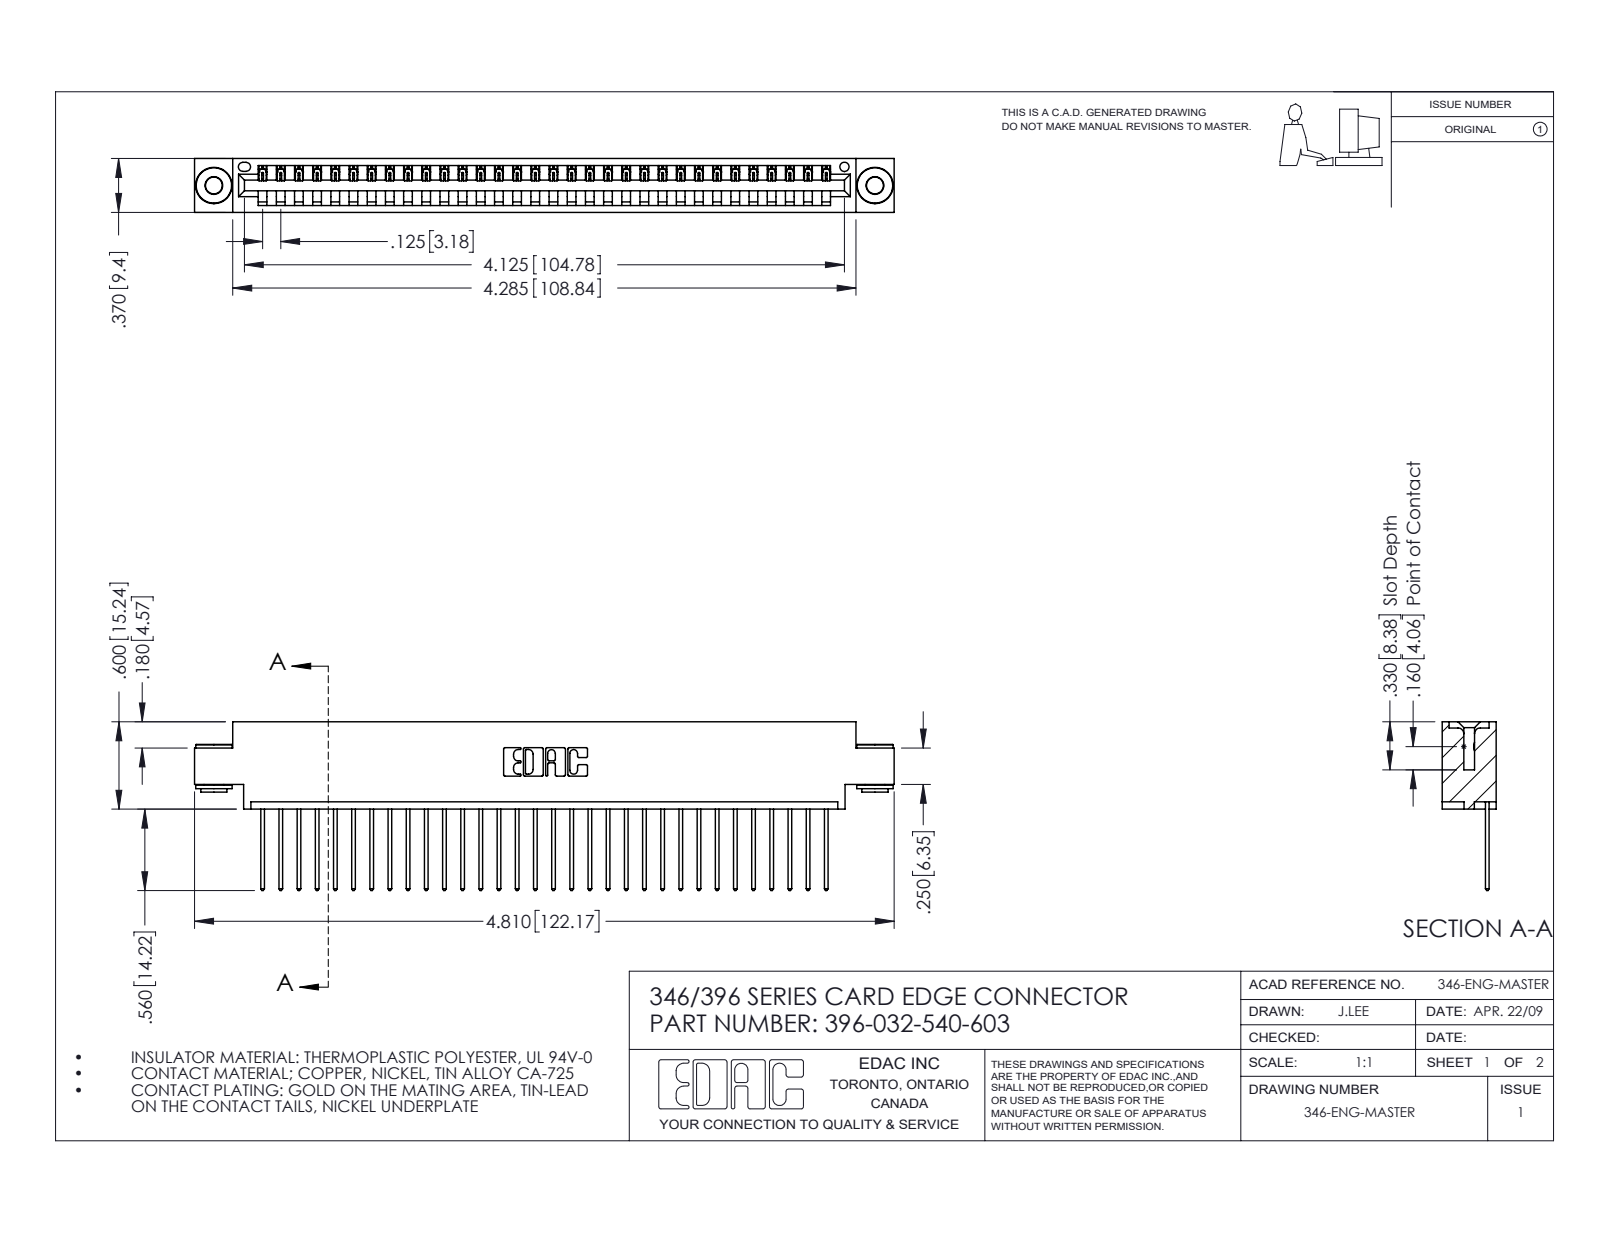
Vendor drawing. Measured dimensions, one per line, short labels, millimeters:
name: 346 Part_0.170 Offset - 0.156 Dia-TH; 396-032-540-603; 345-250-002_345-250-002-102; 345-292-001_345-293-140
written by: SolidWorks 2016 (CONFIG_CONTROL_DESIGN)
unit: mm
bodies: 35 solids, 2020 faces (1370 planar, 642 cylindrical, 8 other)
size: 122.2 × 29.5 × 9.4
volume: 11 500 mm³; area: 15 010 mm²
holes: 2× ⌀2.9, 2× ⌀4, 1× ⌀1.6
bosses: 2× ⌀6.4, 2× ⌀4.6, 2× ⌀3.5
rounds: 64× R0.2, 64× R0.3, 22× R0.3, 6× R0.2, 6× R0.8, 3× R0.7, 2× R0.8, 2× R1
face distances: 1.2, 8.2, 9.4, 6.4, 0.6, 1.8, 7.6, 3.8, 5.6, 2.5
hole spacings: 6.2, 110.2, 115.4
